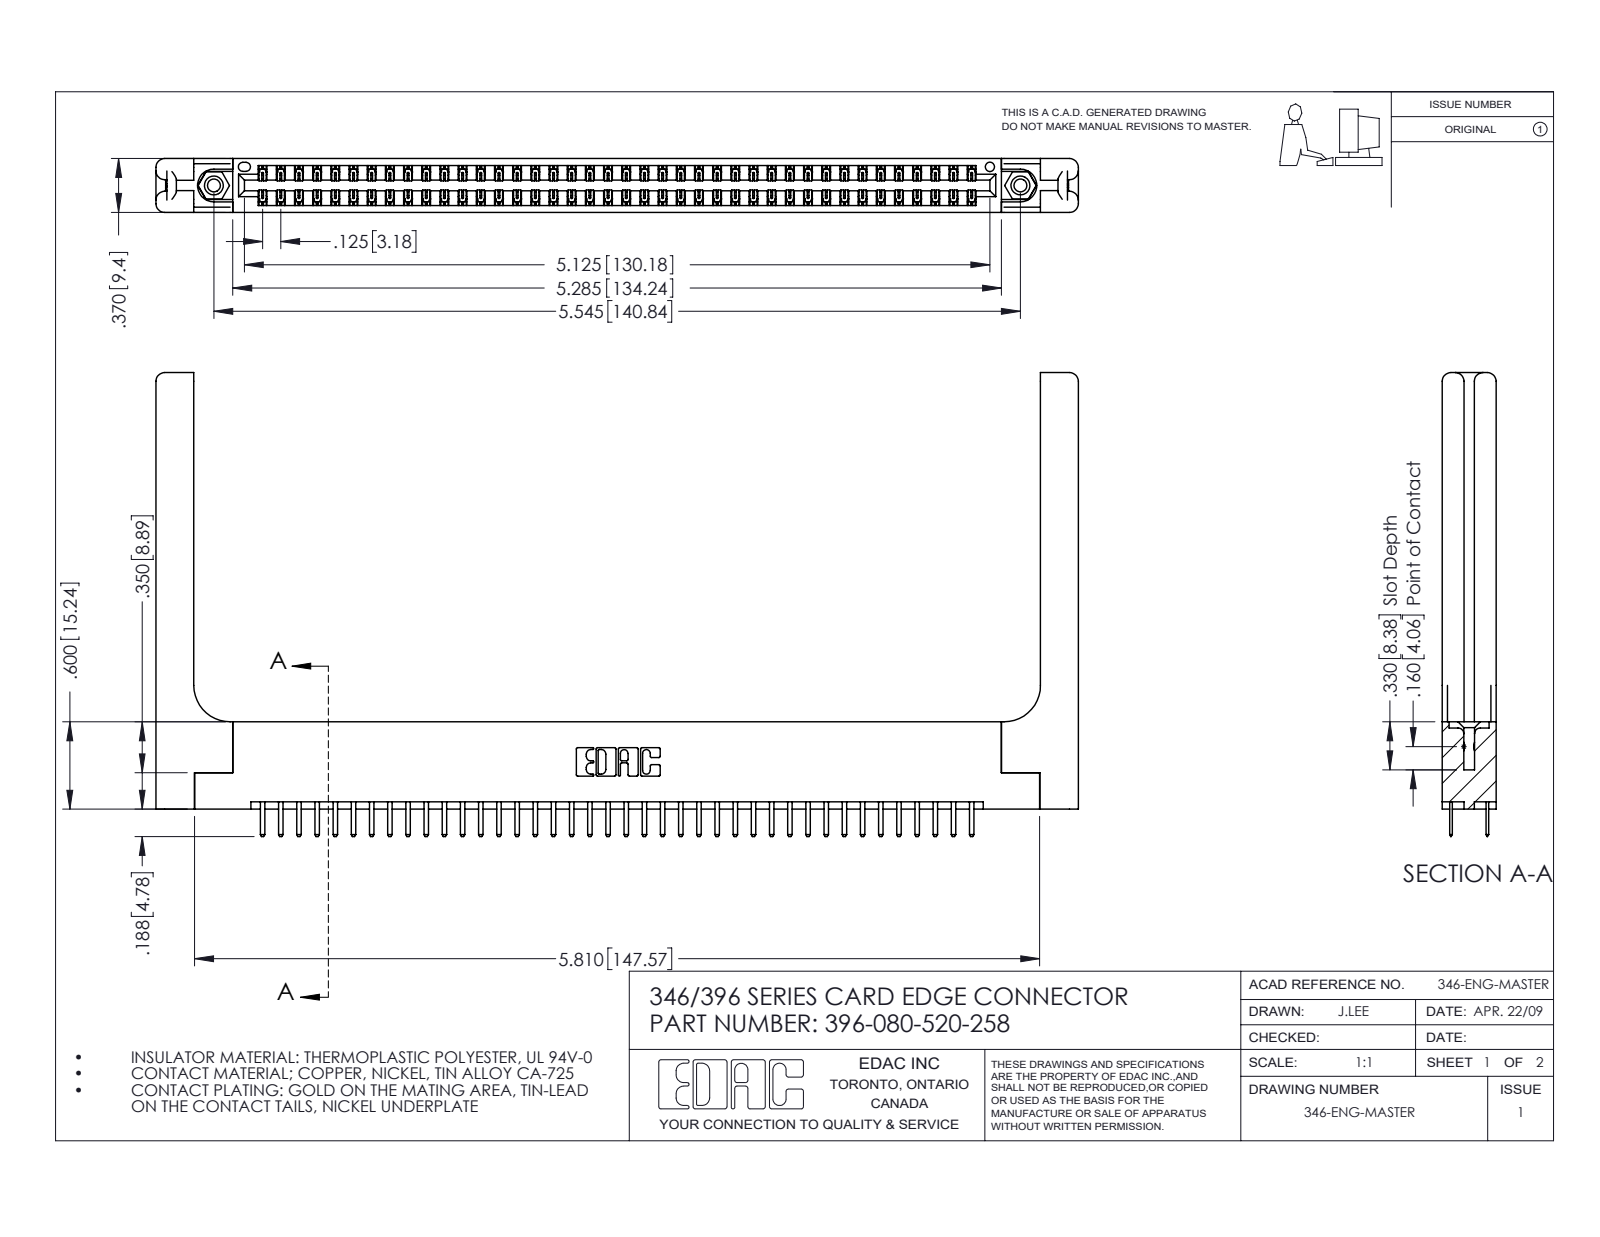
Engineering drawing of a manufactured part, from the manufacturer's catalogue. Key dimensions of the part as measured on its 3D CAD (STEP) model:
Part name (STEP PRODUCT): 345-250-001_345-250-001-102; 346 Part_Flush Mounting Lugs - 0.156 Dia-TH; 346-220-058_345-220-058; 345-292-001_345-293-120 (+1 more)
STEP written by: SolidWorks 2016 (CONFIG_CONTROL_DESIGN)
Units: inches
Bodies: 85 solids, 4858 faces (3184 planar, 1614 cylindrical, 60 other)
Overall size (bounding box): 6.341 × 3.188 × 0.37
Volume: 1.413 in³ · Surface area: 40.89 in²
Round holes (diameter × count): ⌀0.089 ×2, ⌀0.125 ×2, ⌀0.156 ×2, ⌀0.064 ×1
Round bosses / shafts (diameter × count): ⌀0.155 ×2
Partial cylindrical surfaces — rounded edges, fillets, slot ends (radius × count): R0.006 ×120, R0.01 ×84, R0.01 ×22, R0.06 ×16, R0.007 ×6, R0.031 ×6, R0.026 ×3, R0.014 ×2
Main face-to-face distances: 0.37, 0.048, 0.322, 0.072, 0.25, 0.15, 0.148, 0.298, 0.025, 0.275
Hole centre spacings: 0.246, 5.336, 5.545
